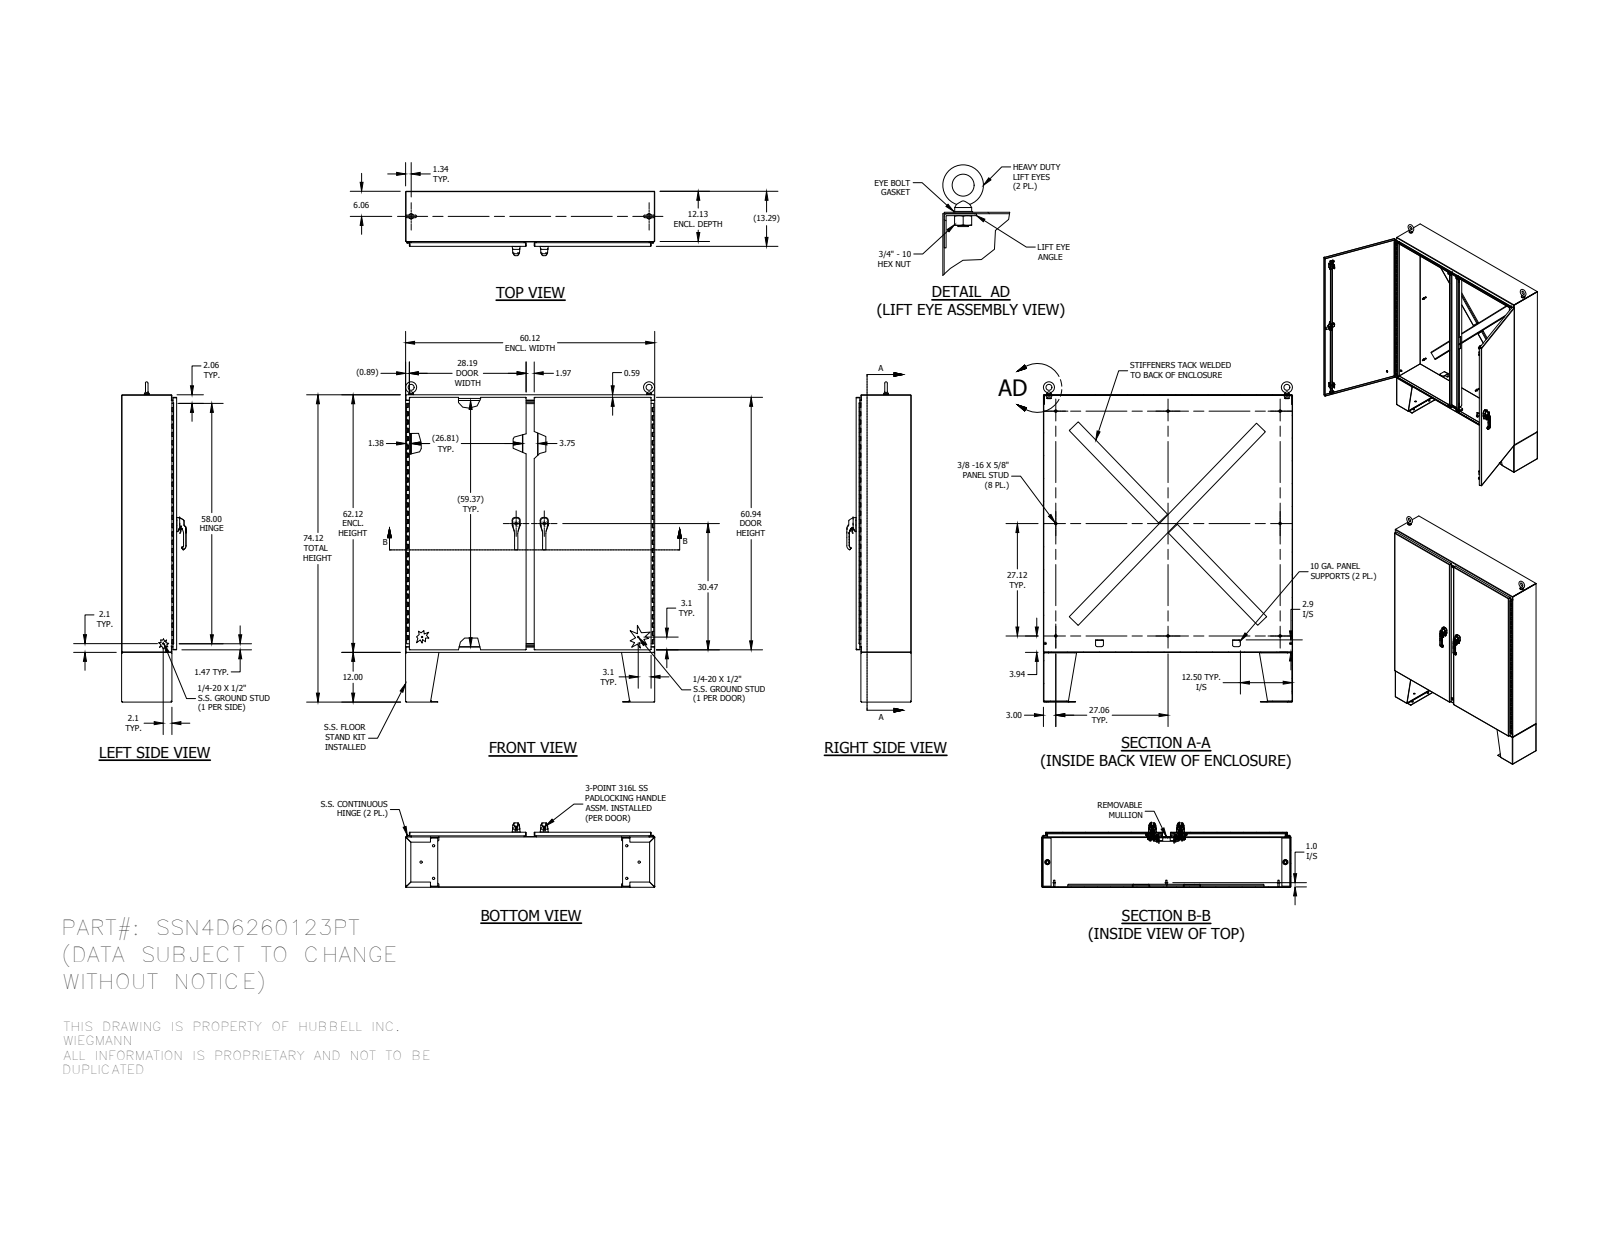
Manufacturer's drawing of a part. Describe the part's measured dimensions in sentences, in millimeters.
The part is named "328131P-58_1; 1091-BR11_AF0_1; HFW31712_1; 38846_1 (+8 more)". Its 3-D file was written by "SolidWorks 2014 (AUTOMOTIVE_DESIGN)". It is 138 solids with 7184 faces: 2696 planar, 2772 cylindrical and 1716 other. Overall it measures 1962.1 by 1527.2 by 394.7 millimeters. Its volume is 21 840 000 cubic millimeters and its surface area 17 960 000 square millimeters. Round holes: 18 of diameter 14.3, 16 of diameter 6.7, 16 of diameter 9.5, 8 of diameter 4.7, 6 of diameter 5.4, 6 of diameter 7.1, 5 of diameter 6.4, 4 of diameter 5, 4 of diameter 6.1, 4 of diameter 6.4, 4 of diameter 7.1, 4 of diameter 8. Round bosses or shafts: 10 of diameter 8.4, 8 of diameter 15.9, 7 of diameter 6.4, 6 of diameter 13.5, 6 of diameter 6, 5 of diameter 25.4, 4 of diameter 14.3, 4 of diameter 13.5. Partial cylindrical surfaces (rounded edges, fillets, slot ends): 350 of radius 0.5, 213 of radius 0.3, 46 of radius 3.2, 44 of radius 0.5, 34 of radius 1.3, 32 of radius 0.8, 28 of radius 2, 24 of radius 0.6. The main face-to-face distances are 2.4, 335.2, 335.1, 332.8, 332.7, 337.6, 2.4, 337.5, 2.3, 1524.8. The hole center spacings are 163.7, 9.7, 9.7, 19.3, 327.4, 1322.1, 1331.6, 1341.2.
